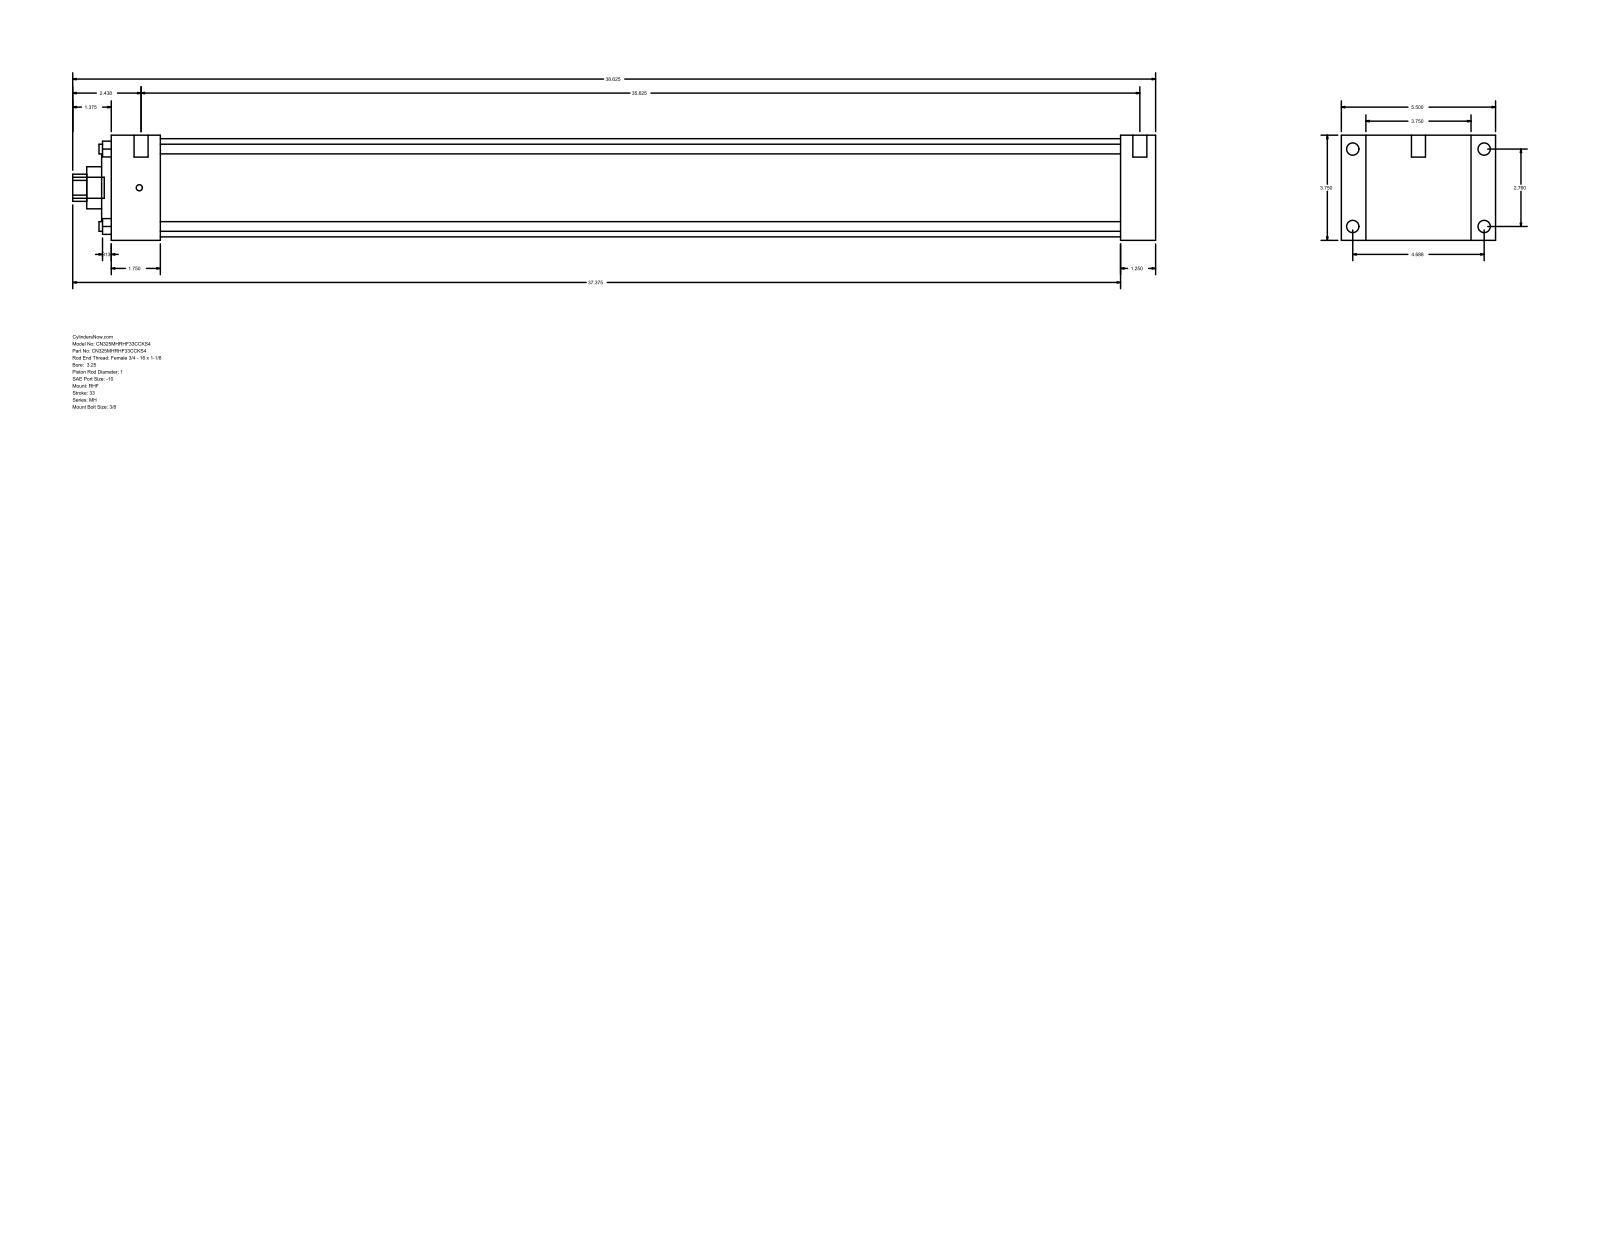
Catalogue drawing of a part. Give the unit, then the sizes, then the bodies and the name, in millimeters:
Units: millimetres
Overall size (bounding box): 981.08 × 139.7 × 95.25
Round holes (diameter × count): ⌀8.76 ×4, ⌀25.4 ×1, ⌀38.1 ×1, ⌀60.33 ×1, ⌀88.9 ×1
Round bosses / shafts (diameter × count): ⌀11.13 ×4, ⌀5.56 ×4, ⌀12.7 ×2, ⌀19.05 ×1
Partial cylindrical surfaces — rounded edges, fillets, slot ends (radius × count): R12.29 ×1
Main face-to-face distances: 95.24, 31.75, 22.23, 117.47, 914.41, 946.16, 139.7, 44.46, 869.95, 901.7
Hole centre spacings: 49.57, 70.1, 99.14
Bodies: 0 solids, 90 faces (61 planar, 29 cylindrical, 0 other)
Part name (STEP PRODUCT): MH_RHF__0325_1
STEP written by: GSSL Pune (CONFIG_CONTROL_DESIGN)
